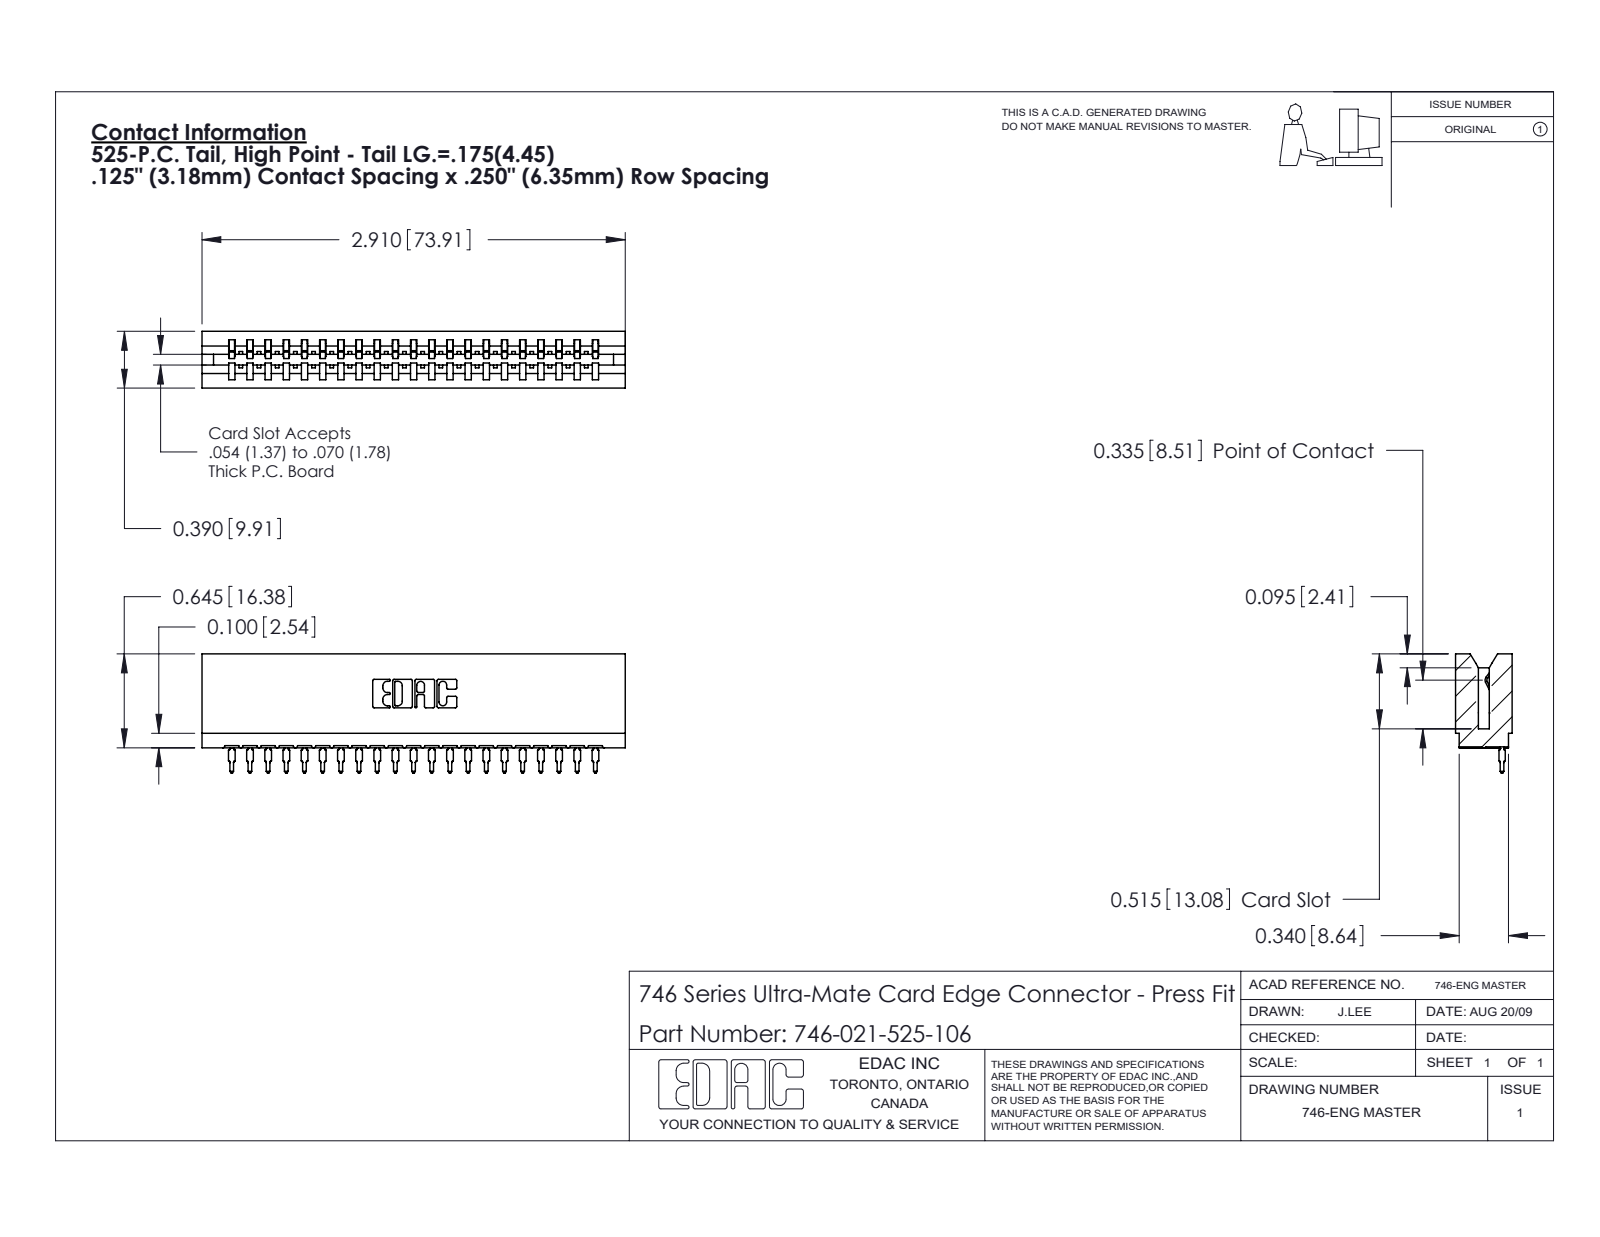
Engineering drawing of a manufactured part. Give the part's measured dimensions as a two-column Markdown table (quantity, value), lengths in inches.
| quantity | value |
| --- | --- |
| part name | 746-292-001_525; 746-021-525-106; 746 Part_.515 Slot Depth - 06 |
| STEP written by | SolidWorks 2020 (CONFIG_CONTROL_DESIGN) |
| units | inches |
| bodies | 22 solids, 2366 faces (1379 planar, 441 cylindrical, 546 other) |
| overall size | 2.91 × 0.819 × 0.39 |
| volume | 0.477 in³ |
| surface area | 17.28 in² |
| partial cylindrical surfaces (radius × count) | 0.021 × 42, 0.01 × 22, 0.015 × 22, 0.007 × 6, 0.031 × 6, 0.005 × 4, 0.011 × 4, 0.026 × 3 |
| main face-to-face distances | 0.057, 0.333, 0.25, 0.39, 0.5, 0.025, 0.307, 0.042, 0.125, 0.375 |
